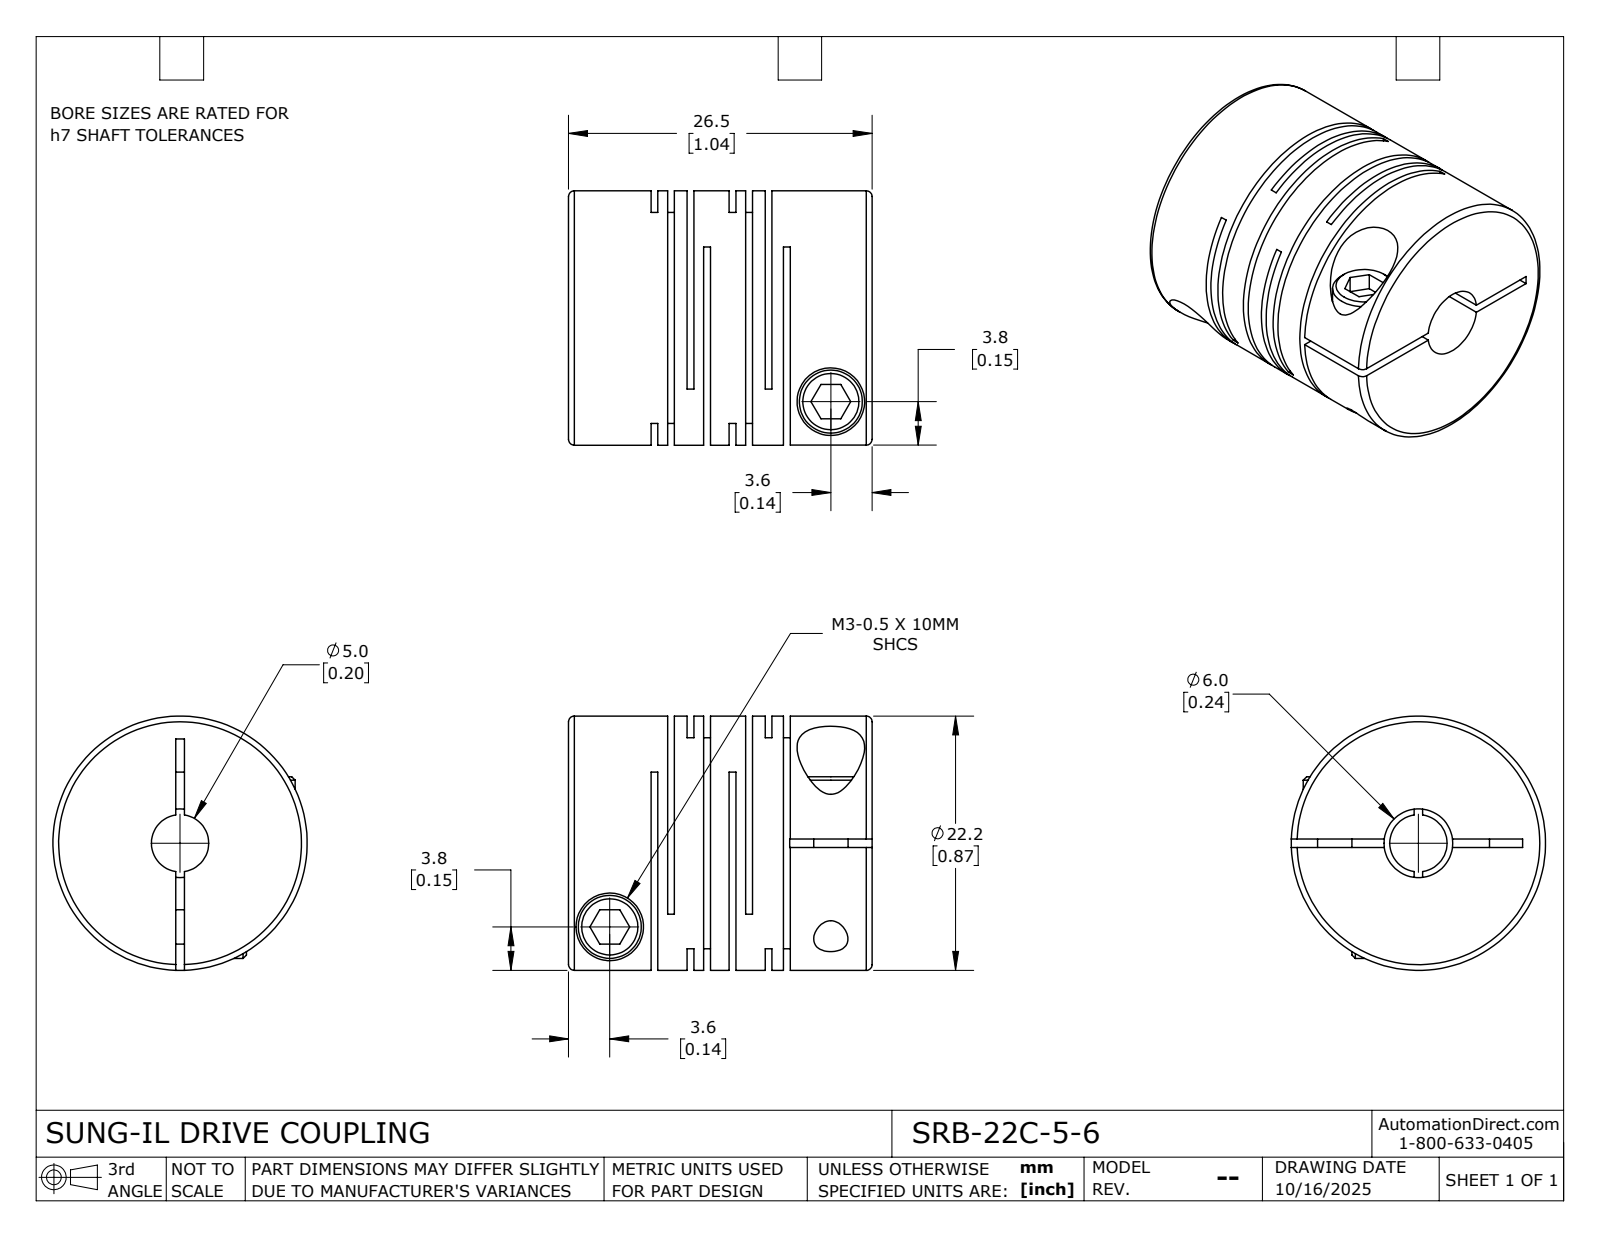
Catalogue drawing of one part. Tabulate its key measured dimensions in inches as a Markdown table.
| quantity | value |
| --- | --- |
| part name | SRB-22C-5-6 |
| STEP written by | SolidWorks 2024 (CONFIG_CONTROL_DESIGN) |
| units | inches |
| bodies | 1 solid, 115 faces (60 planar, 42 cylindrical, 13 other) |
| overall size | 1.043 × 0.874 × 0.874 |
| volume | 0.478 in³ |
| surface area | 12.65 in² |
| round holes (diameter × count) | 0.118 × 2, 0.232 × 2, 0.197 × 1, 0.236 × 1 |
| round bosses / shafts (diameter × count) | 0.217 × 2, 0.874 × 1 |
| main face-to-face distances | 0.023, 0.269, 0.124, 0.057, 0.211, 0.067, 0.144, 0.08, 0.292, 0.245 |
